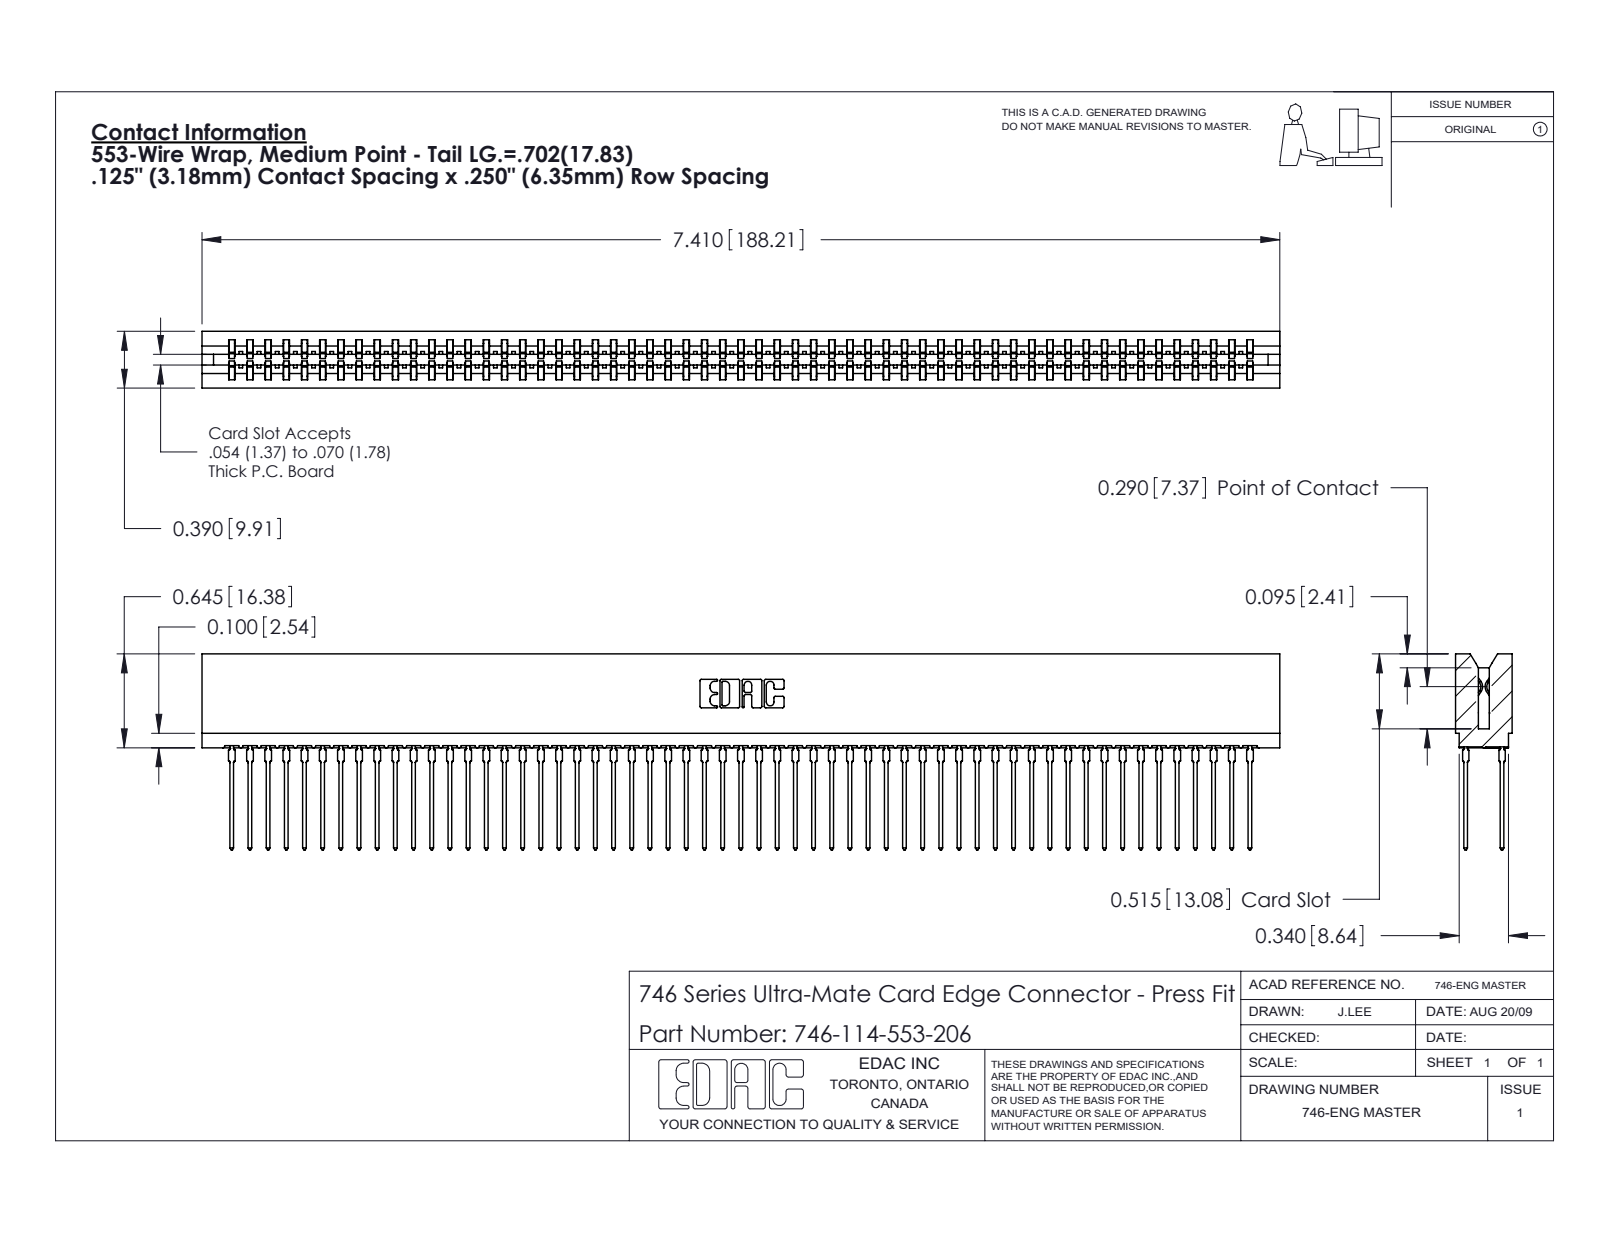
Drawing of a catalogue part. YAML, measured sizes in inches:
part_name: "746-114-553-206; 746 Part_.515 Slot Depth - 06; 746-292-001_553"
step_written_by: "SolidWorks 2020 (CONFIG_CONTROL_DESIGN)"
units: inches
bodies: {solids: 115, faces: 10301, planar: 5300, cylindrical: 2037, other: 2964}
overall_size: [7.41, 1.346, 0.39]
volume: 1.255
surface_area: 55.27
partial_cylinders:
  - {radius: 0.021, count: 228}
  - {radius: 0.015, count: 58}
  - {radius: 0.01, count: 22}
  - {radius: 0.005, count: 8}
  - {radius: 0.011, count: 8}
  - {radius: 0.007, count: 6}
  - {radius: 0.031, count: 6}
  - {radius: 0.026, count: 3}
face_to_face_distances: [0.057, 0.333, 0.25, 0.025, 0.307, 0.39, 0.083, 0.275, 0.174, 0.158]
